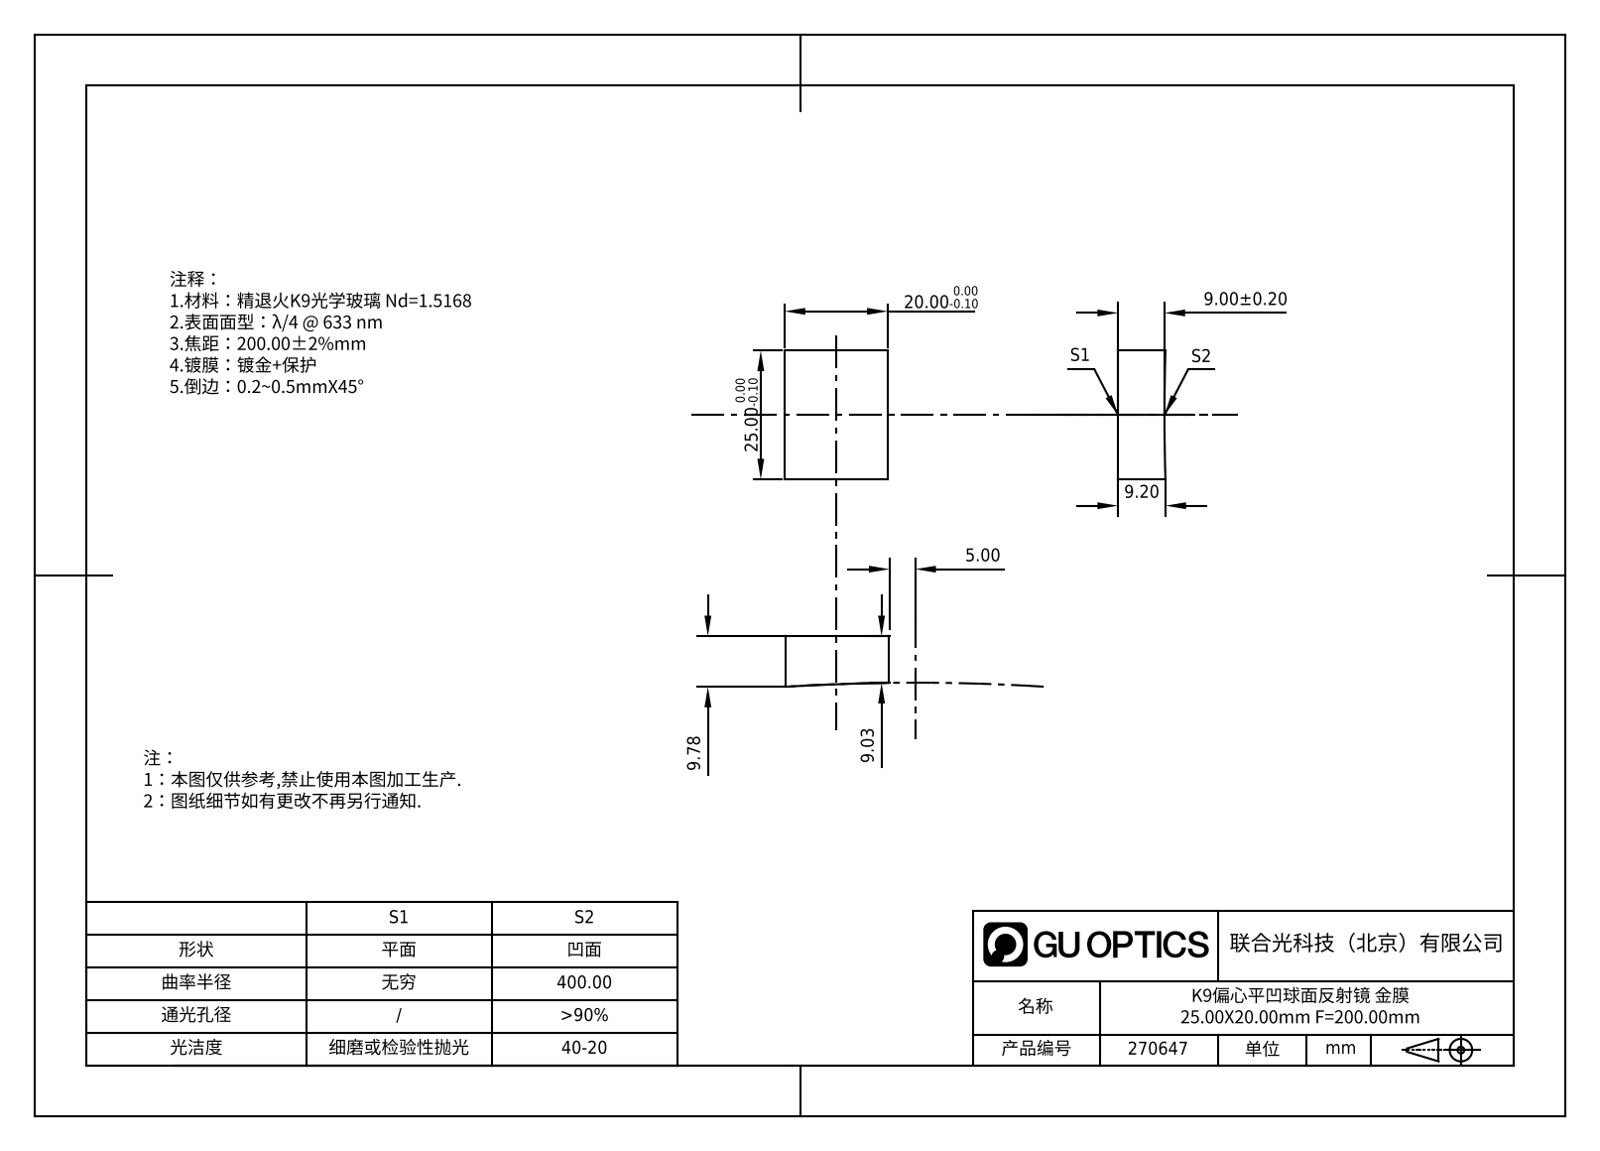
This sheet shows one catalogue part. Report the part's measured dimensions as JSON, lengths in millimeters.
{"part_name": "270647", "step_written_by": "SolidWorks 2020 (CONFIG_CONTROL_DESIGN)", "units": "millimeters", "bodies": {"solids": 1, "faces": 7, "planar": 5, "cylindrical": 0, "other": 2}, "overall_size": [25, 20, 9.98], "volume_mm3": 4694, "surface_area_mm2": 1855, "face_to_face_distances": [20, 25]}
